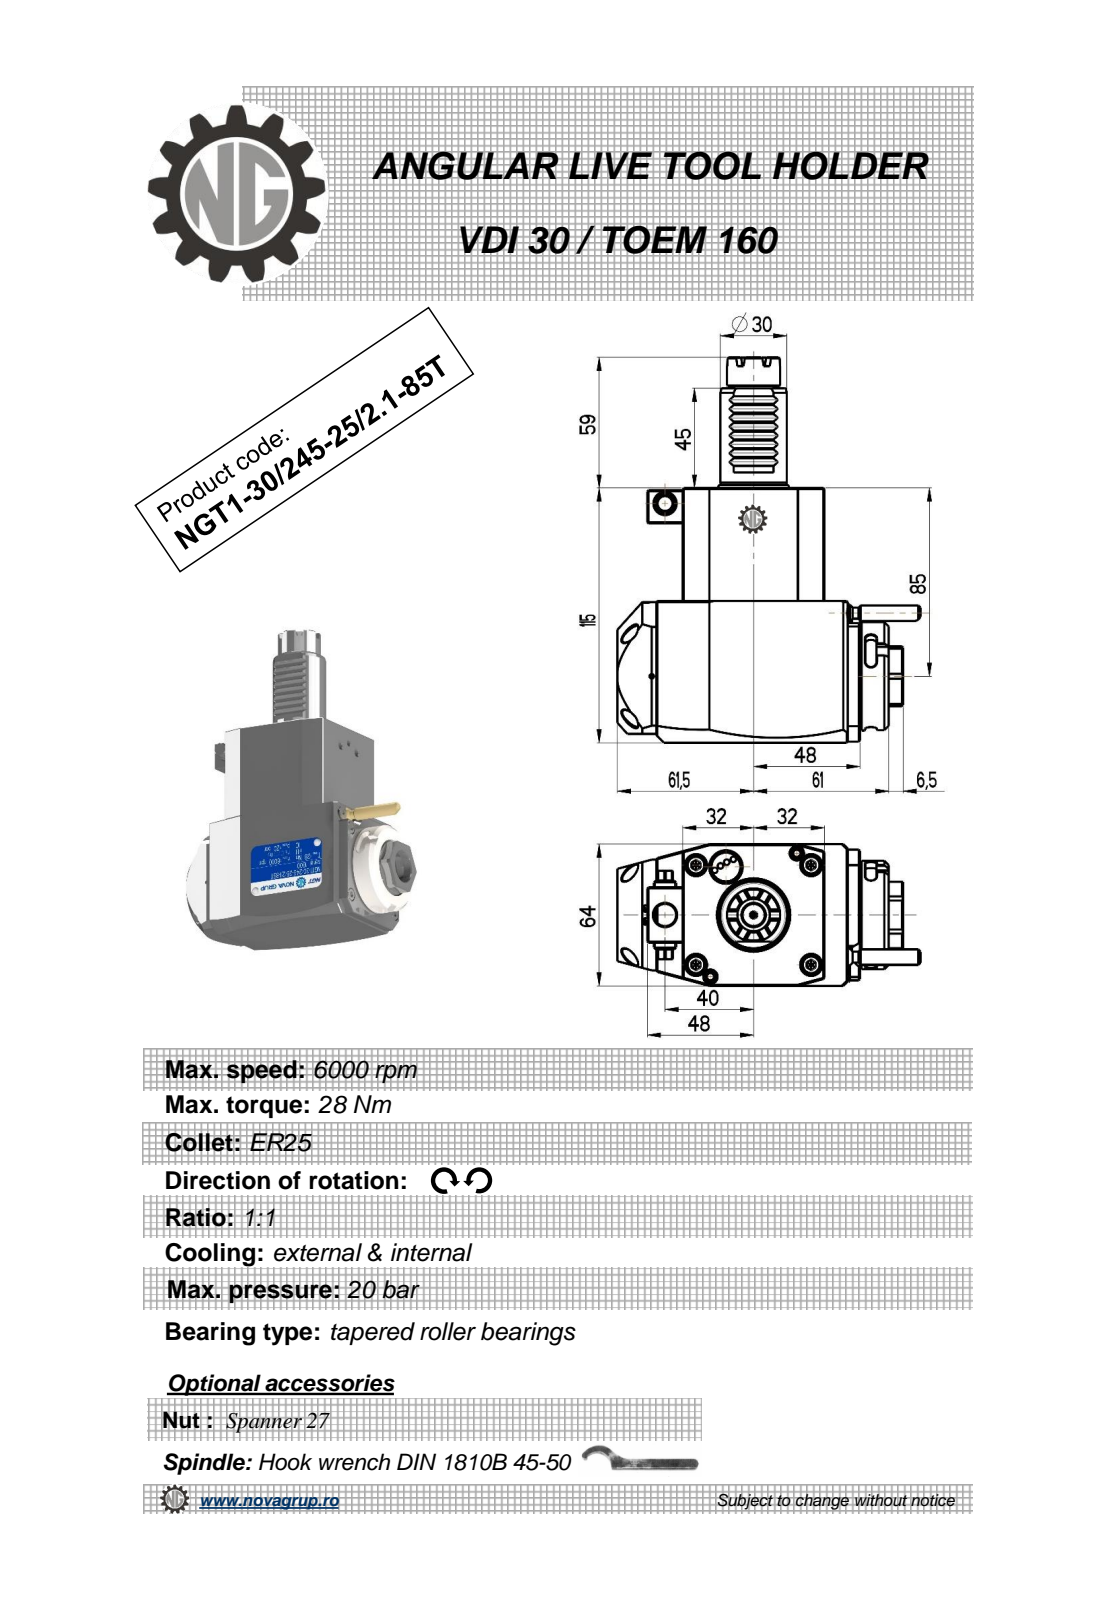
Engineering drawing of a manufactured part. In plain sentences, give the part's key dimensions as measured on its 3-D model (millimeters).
The part is named "NGT1_30_245_25_1_1_85T". Its 3-D file was written by "PRO/ENGINEER BY PARAMETRIC TECHNOLOGY CORPORATION, 2010280 (CONFIG_CONTROL_DESIGN)". It is 1 solid with 374 faces: 210 planar, 82 cylindrical and 82 other. Overall it measures 174 by 136.88 by 64 millimeters. Its volume is 673 046 cubic millimeters and its surface area 57 601 square millimeters. Round holes: 1 of diameter 2.5, 1 of diameter 3, 1 of diameter 8.5, 1 of diameter 9.5, 1 of diameter 10, 1 of diameter 18. Round bosses or shafts: 2 of diameter 8, 1 of diameter 49, 1 of diameter 42, 1 of diameter 30, 1 of diameter 24, 1 of diameter 17.7, 1 of diameter 15.2, 1 of diameter 10. Partial cylindrical surfaces (rounded edges, fillets, slot ends): 8 of radius 0.3, 6 of radius 2.5, 2 of radius 180, 1 of radius 3.85, 1 of radius 4.5, 1 of radius 15, 1 of radius 21.5, 1 of radius 33.5. The main face-to-face distances are 64, 115, 16, 80, 13, 51, 29.5, 93.5, 109.5, 72.18. The hole center spacings are 34.25, 51.62, 76.5.
